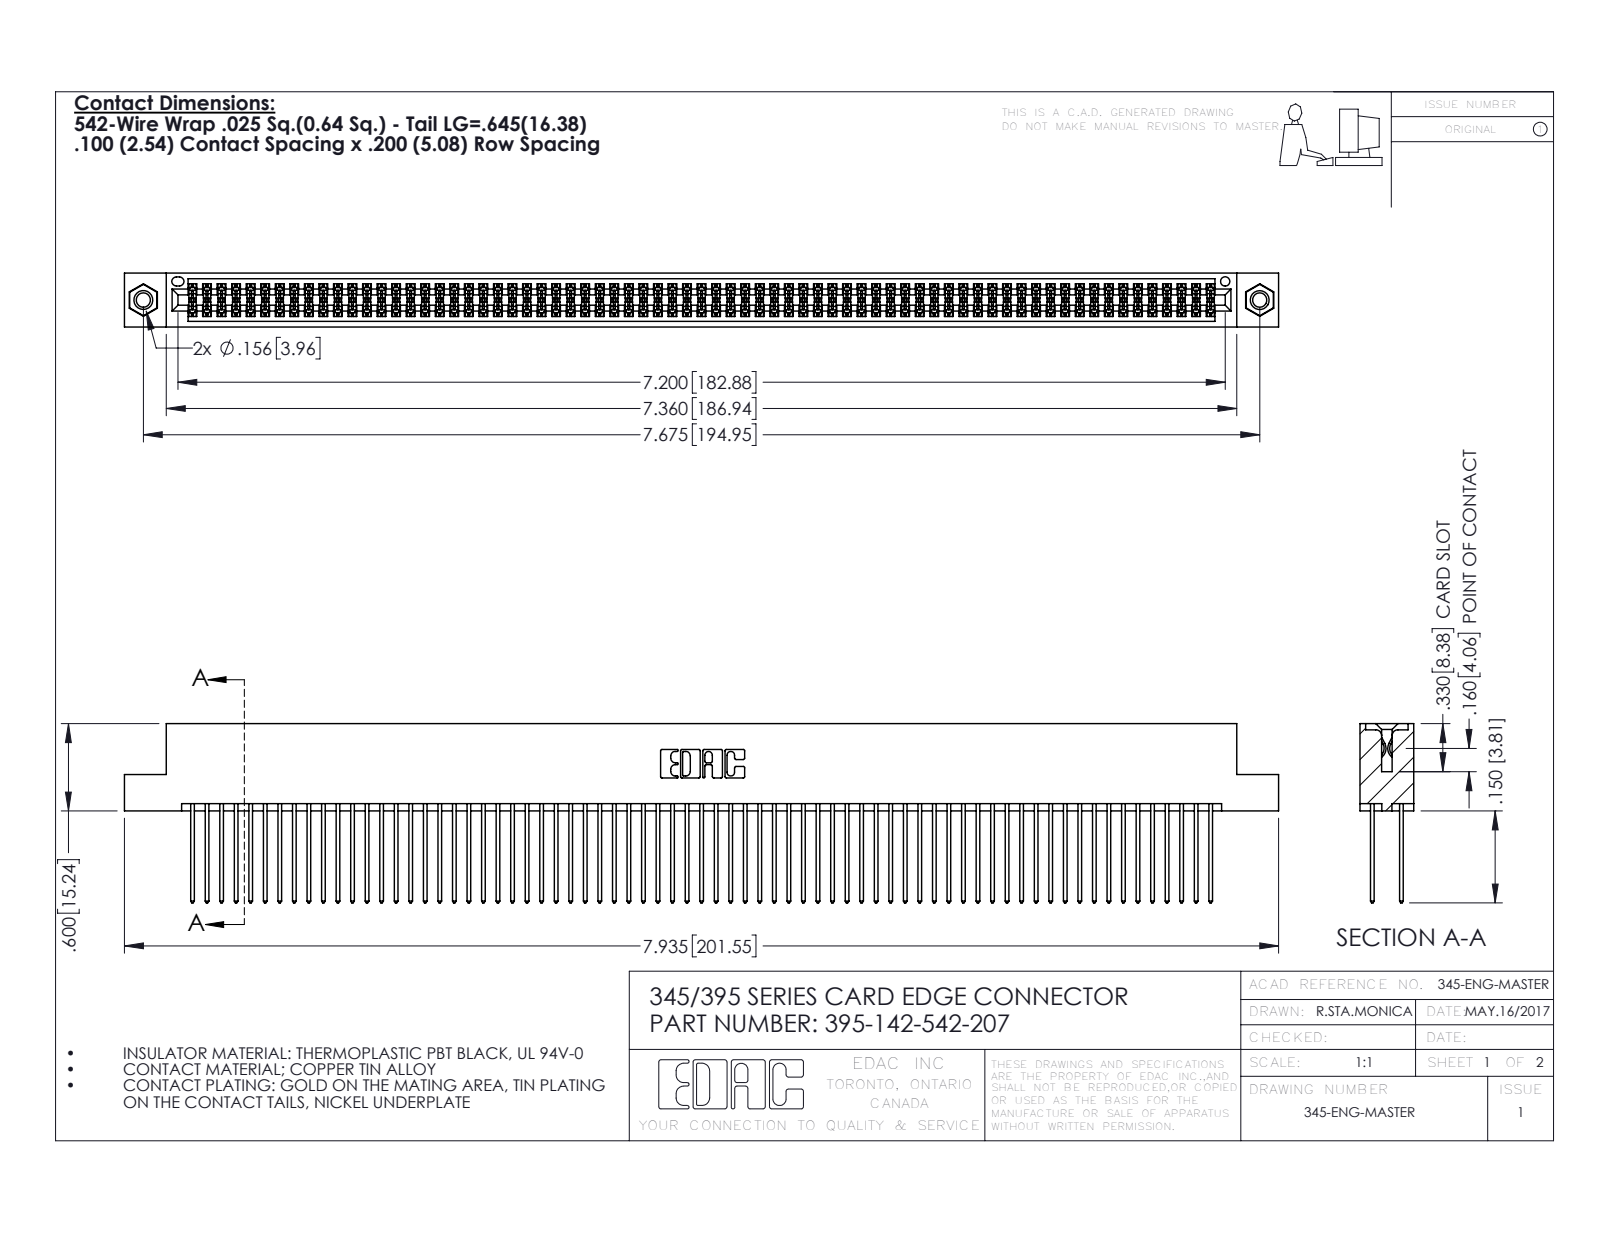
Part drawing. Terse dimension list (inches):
name: 345 Part_Flush Mounting Lugs - 0.156 Dia-TI; 345-292-001_345-293-142; 345-250-001_345-250-005-103; 395-142-542-207
written by: SolidWorks 2016 (CONFIG_CONTROL_DESIGN)
unit: in
bodies: 145 solids, 7286 faces (4798 planar, 2472 cylindrical, 16 other)
size: 7.935 × 1.232 × 0.37
volume: 1.251 in³; area: 52.67 in²
holes: 2× ⌀0.098, 2× ⌀0.125, 2× ⌀0.156, 1× ⌀0.064
bosses: 2× ⌀0.155
rounds: 213× R0.006, 142× R0.01, 22× R0.01, 6× R0.007, 6× R0.031, 3× R0.026, 2× R0.014, 2× R0.019
face distances: 0.072, 0.298, 0.2, 0.098, 0.272, 0.025, 0.225, 0.37, 0.175, 0.149
hole spacings: 0.27, 7.439, 7.675
